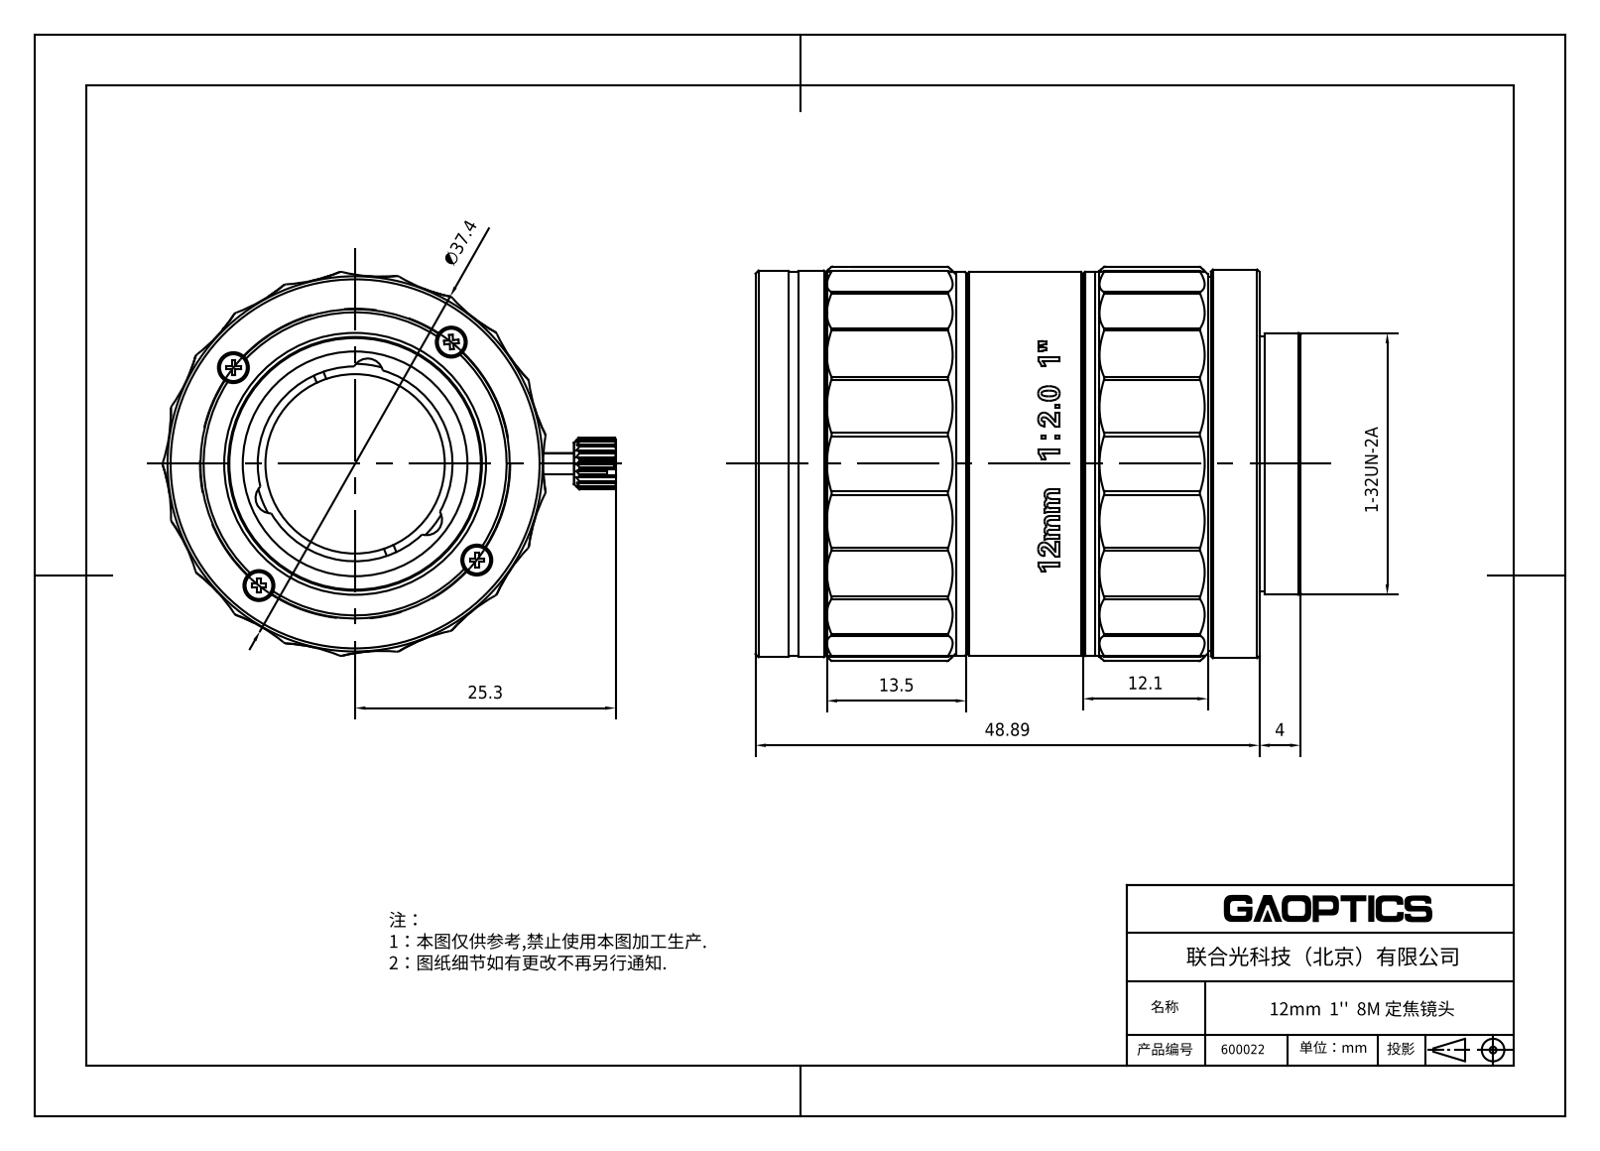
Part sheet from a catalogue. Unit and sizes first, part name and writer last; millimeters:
Units: millimetres
Overall size (bounding box): 53.61 × 45.37 × 38.13
Round holes (diameter × count): ⌀1.6 ×4, ⌀2.85 ×4, ⌀15.11 ×1, ⌀18.51 ×1, ⌀19.51 ×1, ⌀22 ×1, ⌀25.4 ×1, ⌀26 ×1, ⌀26.4 ×1, ⌀29.99 ×1, ⌀35.1 ×1, ⌀36.6 ×1
Round bosses / shafts (diameter × count): ⌀2.8 ×4, ⌀2 ×2, ⌀37.7 ×1, ⌀37.5 ×1, ⌀37.34 ×1, ⌀37.2 ×1, ⌀36.3 ×1, ⌀35.78 ×1
Partial cylindrical surfaces — rounded edges, fillets, slot ends (radius × count): R0.5 ×28, R12.5 ×21, R14 ×21, R2.25 ×2, R18.52 ×1
Main face-to-face distances: 2.2, 0.8, 48.7, 3, 45.7, 47, 44, 1.7, 44.8, 46.5
Hole centre spacings: 16, 22.63, 25.45, 32
Volume: 53 316 mm³ · Surface area: 13 650 mm²
Bodies: 3 solids, 1052 faces (380 planar, 255 cylindrical, 417 other)
Part name (STEP PRODUCT): 600022
STEP written by: SolidWorks 2020 (CONFIG_CONTROL_DESIGN)
